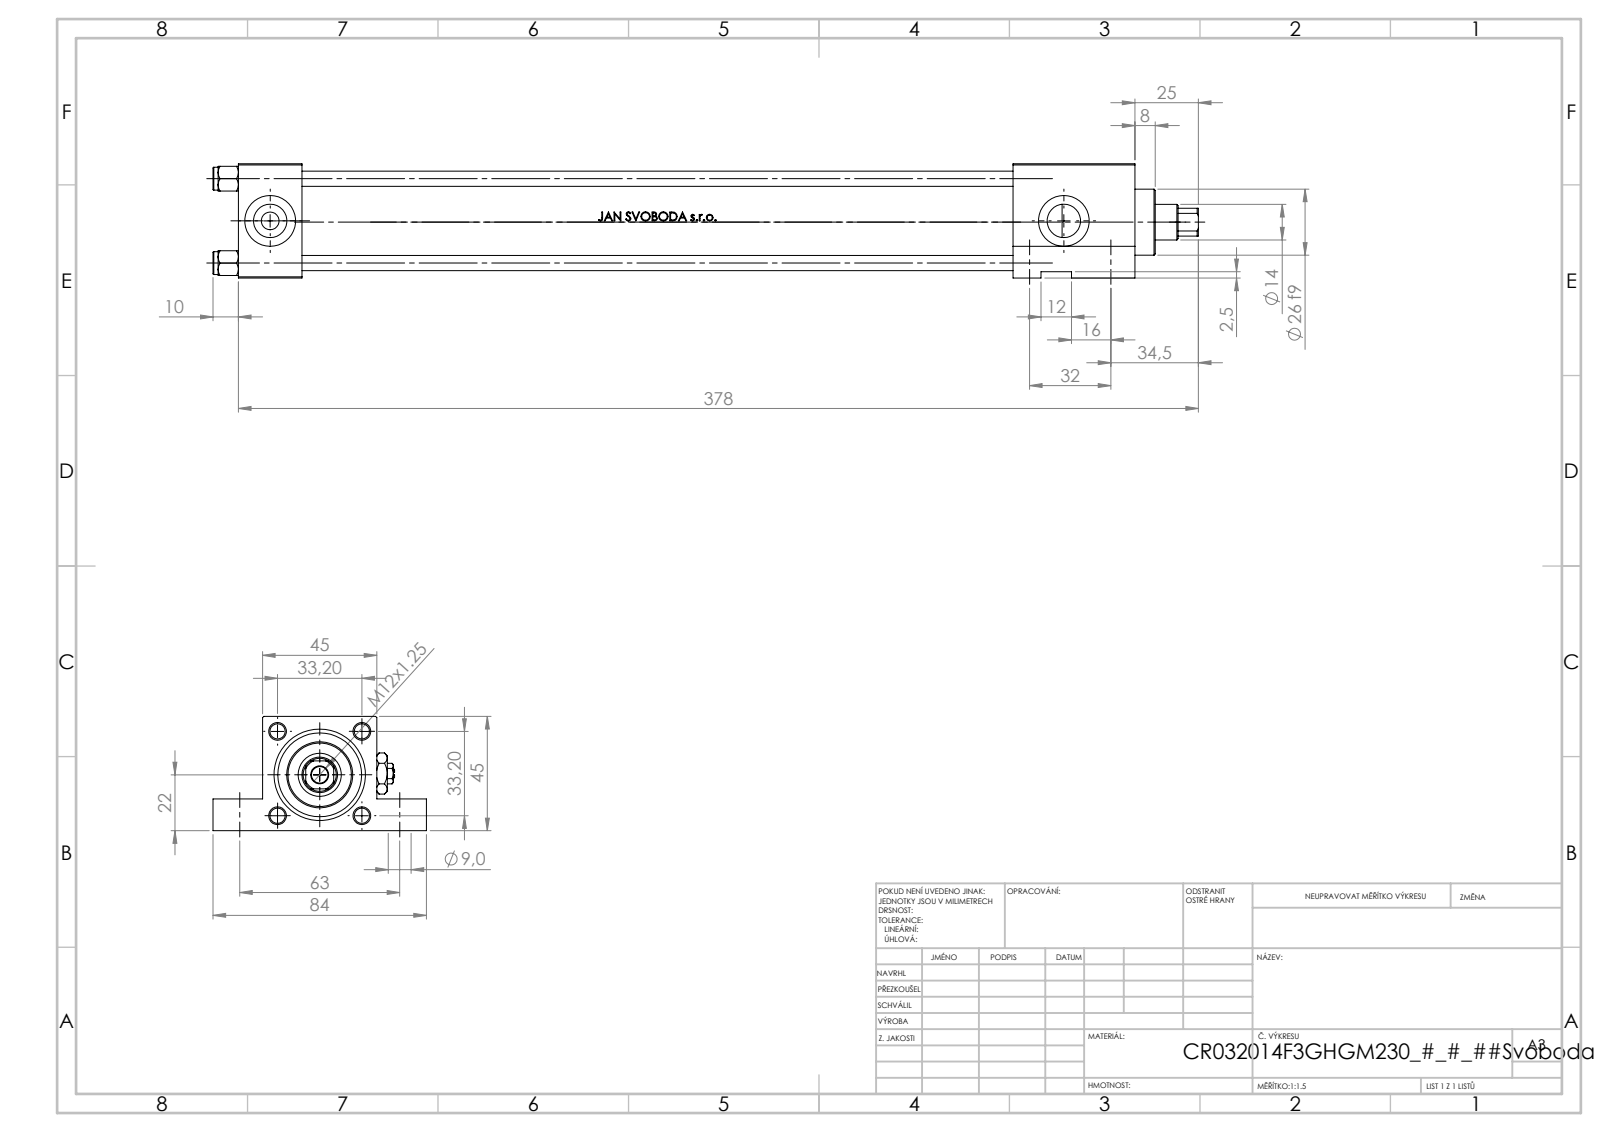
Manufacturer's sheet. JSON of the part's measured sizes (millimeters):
{"part_name": "V215_VC_A; Zatka_pro_OIL_PORT; V215CR_VCP_F; NUT_M5_F (+2 more)", "step_written_by": "SolidWorks 2019 (CONFIG_CONTROL_DESIGN)", "units": "millimeters", "bodies": {"solids": 13, "faces": 1198, "planar": 482, "cylindrical": 134, "other": 582}, "overall_size": [388, 84, 45], "volume_mm3": 347680, "surface_area_mm2": 152525, "round_holes": [[6, 4], [9, 4], [13.16, 3], [20, 3], [7, 2], [6.5, 1], [13, 1], [14, 1], [17, 1], [24, 1], [32, 1], [33, 1]], "round_bosses_or_shafts": [[9, 4], [38, 1], [26, 1]], "partial_cylinders_radius": [[6.5, 1]], "face_to_face_distances": [45, 25, 328, 353, 32.5, 305, 280, 48, 12.5, 10], "hole_center_spacings": [33.2, 23.13, 23.83, 32, 46.95, 63, 70.66, 7]}
